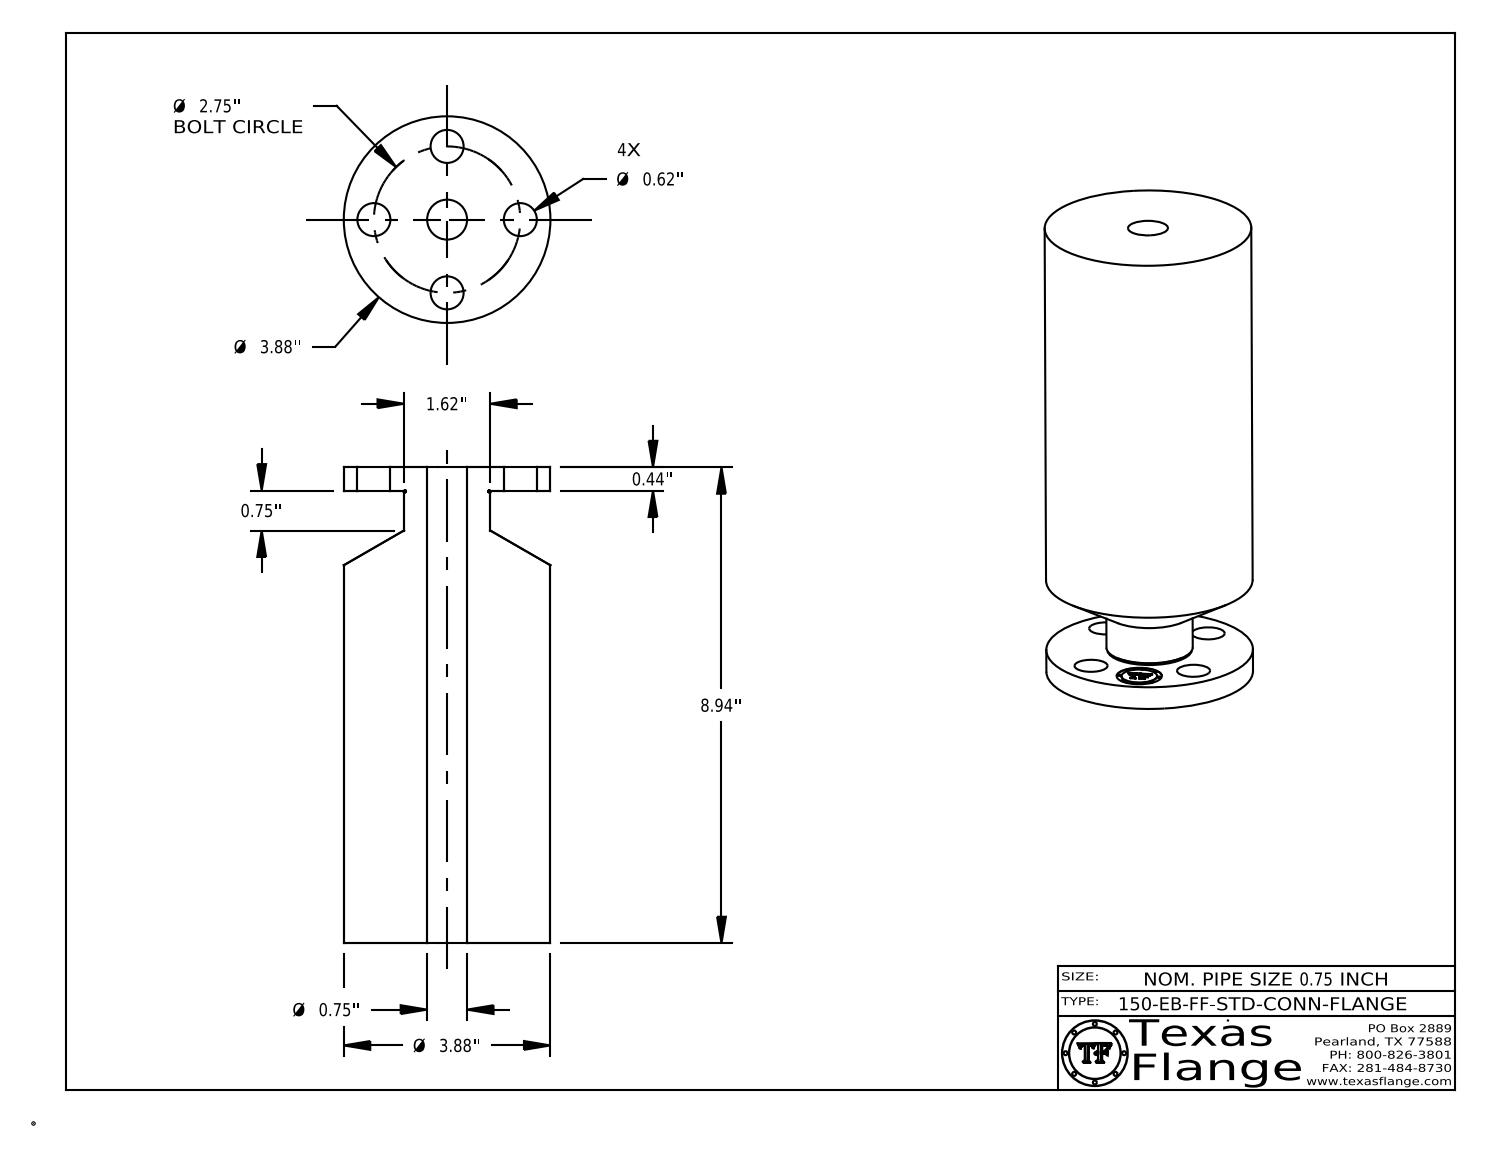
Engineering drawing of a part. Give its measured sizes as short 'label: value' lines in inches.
name: 0.75-150-EB-FF-STD-CONN-FLANGE
written by: CATIA V5 STEP AP214 (AUTOMOTIVE_DESIGN)
unit: in
bodies: 1 solid, 410 faces (368 planar, 36 cylindrical, 6 other)
size: 8.938 × 3.88 × 3.88
volume: 90.25 in³; area: 161.8 in²
holes: 4× ⌀0.62, 1× ⌀0.75, 1× ⌀0.85
bosses: 8× ⌀0.051, 1× ⌀3.88, 1× ⌀1.62, 1× ⌀0.67
face distances: 8.937, 0.437, 8.5, 0.433, 8.505, 0.254, 0.248, 0.016, 0.046, 0.165
hole spacings: 1.375, 1.945, 1.052, 2.541, 2.75
